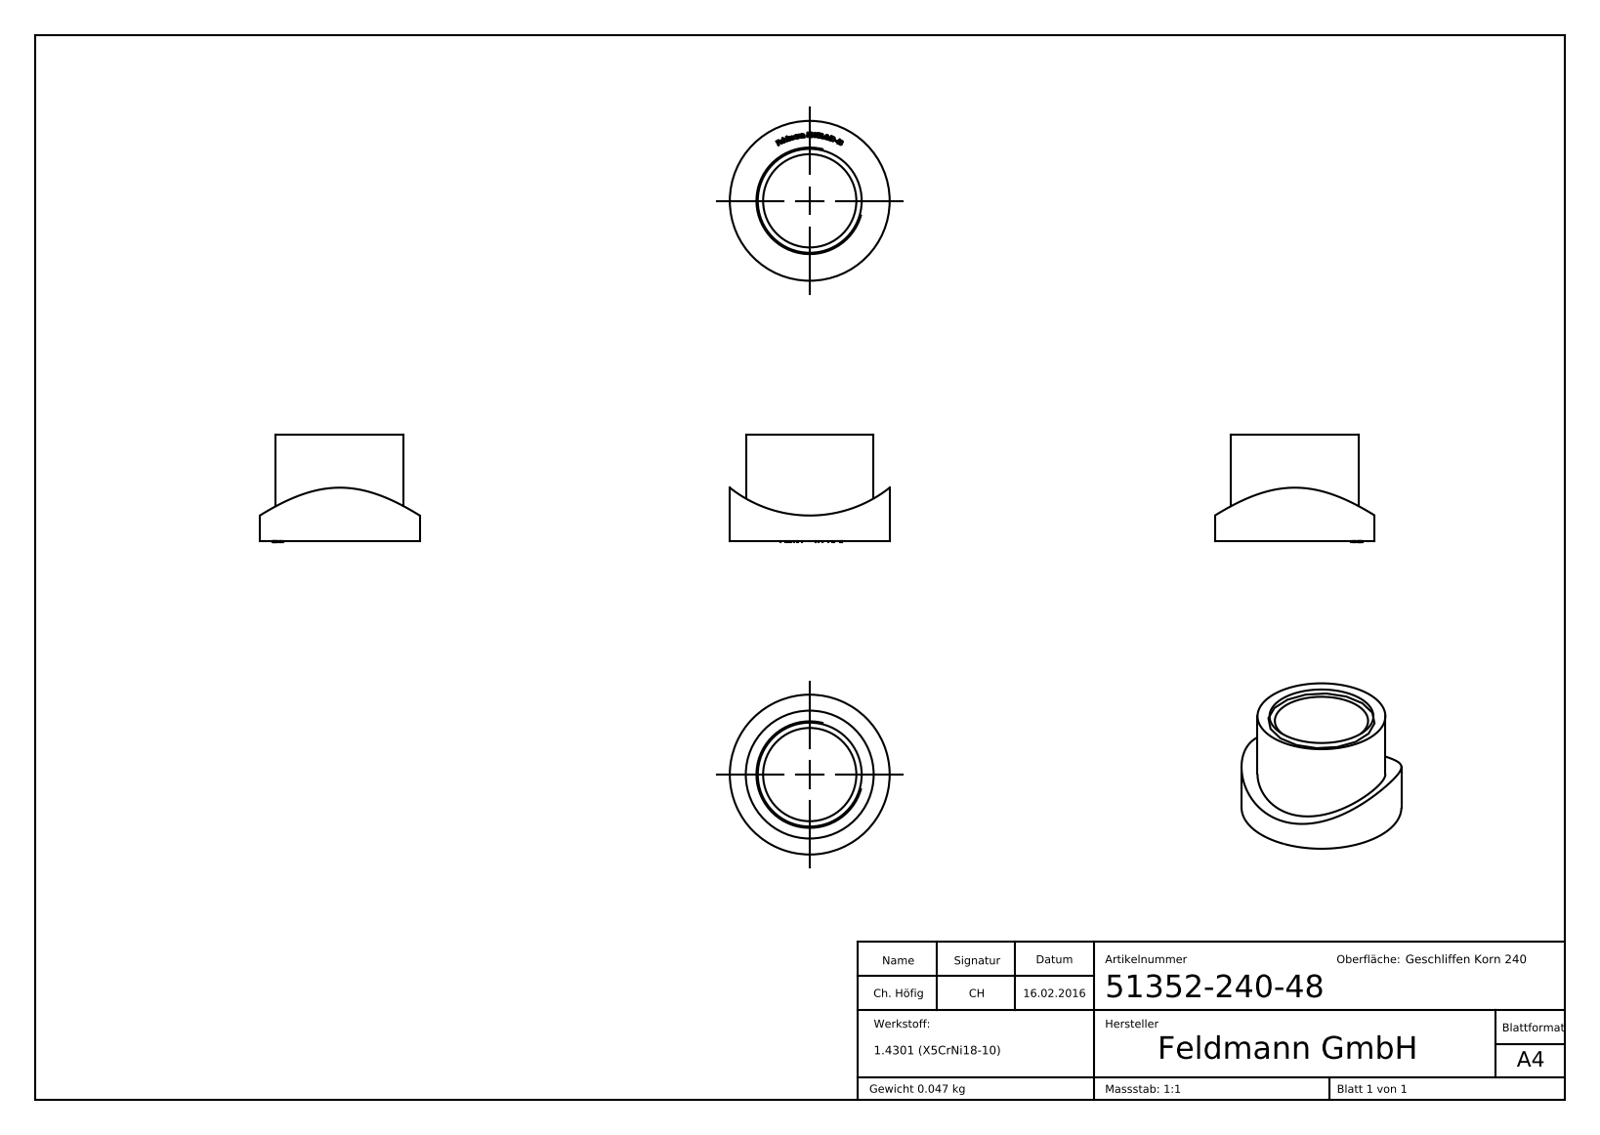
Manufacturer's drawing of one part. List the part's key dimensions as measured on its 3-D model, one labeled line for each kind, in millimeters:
Part name (STEP PRODUCT): 51352-240-48
STEP written by: SolidWorks 2015 (CONFIG_CONTROL_DESIGN)
Units: millimetres
Bodies: 1 solid, 278 faces (151 planar, 7 cylindrical, 120 other)
Overall size (bounding box): 30 × 30 × 20
Volume: 5 947 mm³ · Surface area: 3 723 mm²
Round holes (diameter × count): ⌀17.5 ×1
Round bosses / shafts (diameter × count): ⌀30 ×1, ⌀24 ×1
Partial cylindrical surfaces — rounded edges, fillets, slot ends (radius × count): R24.15 ×1
Main face-to-face distances: 20, 19.9, 0.4, 0.32, 0.43, 0.36, 1.17, 2.53, 0.79, 0.39
